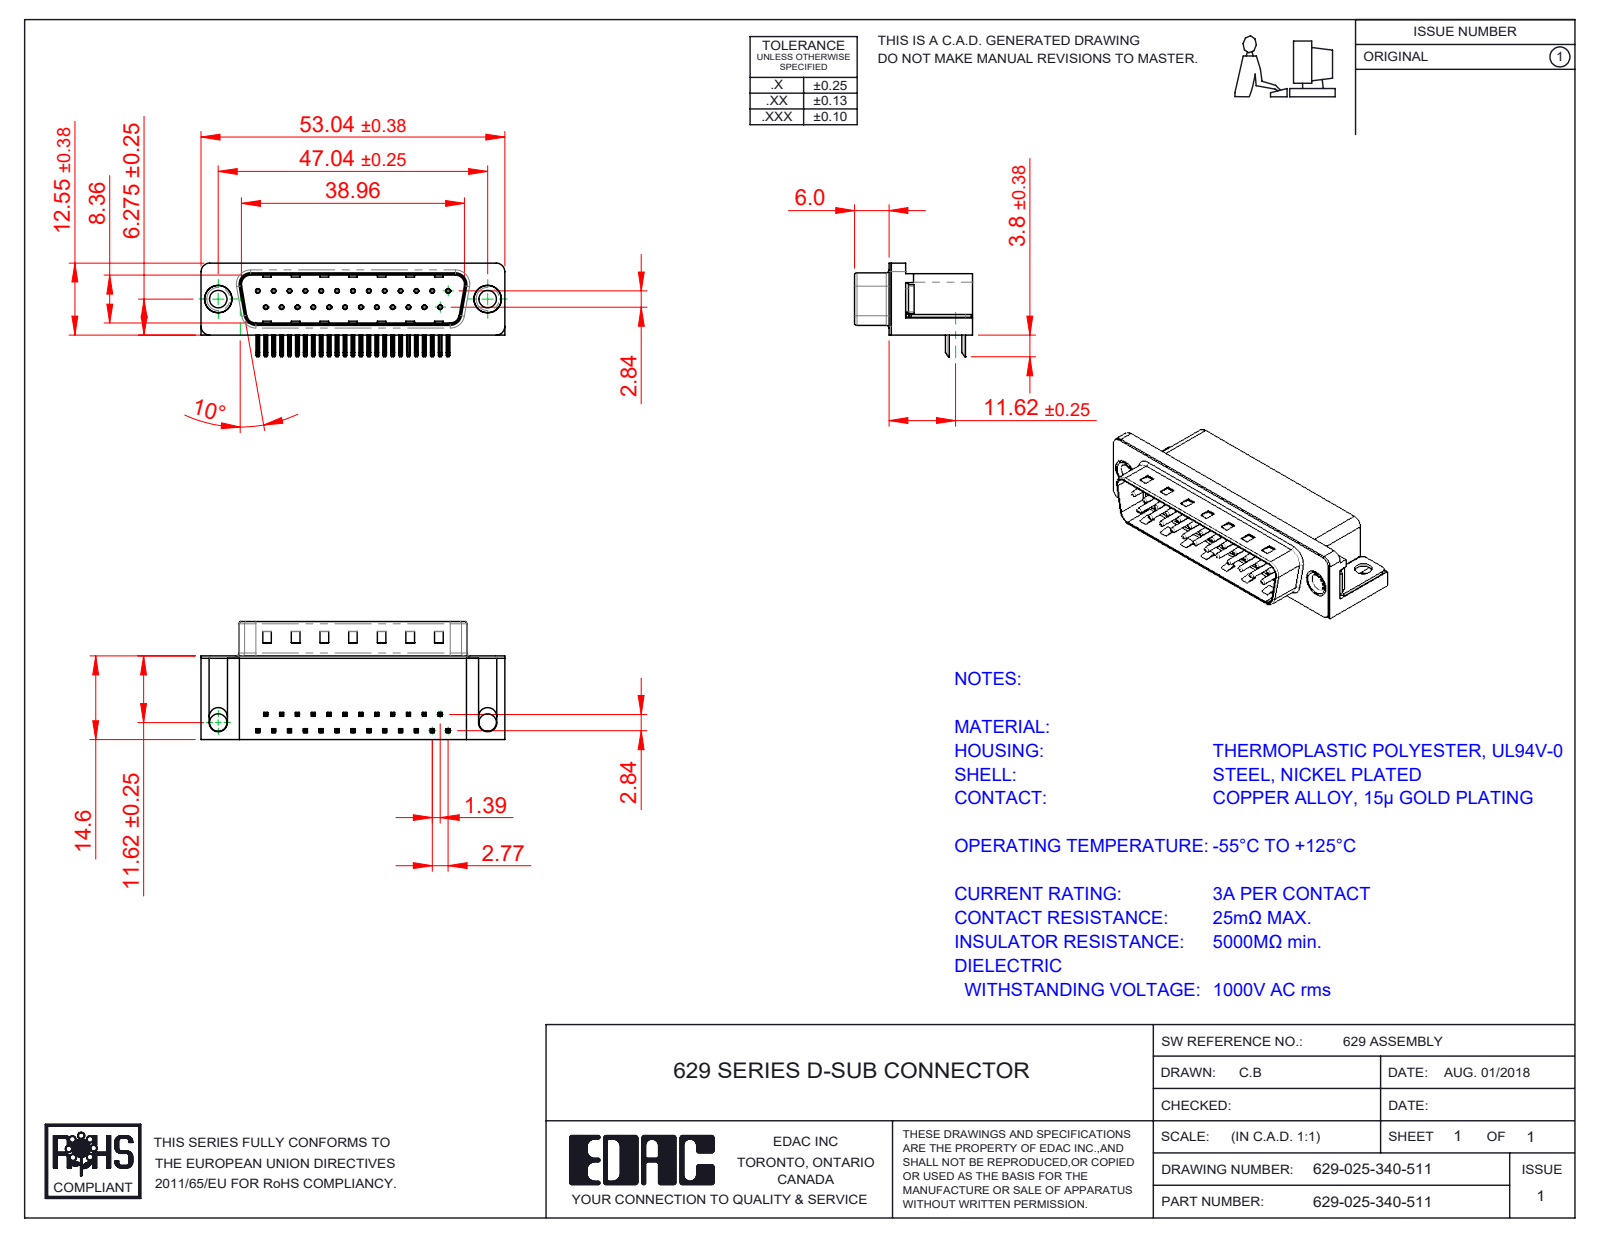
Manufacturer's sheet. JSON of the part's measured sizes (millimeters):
{"part_name": "629 Shell_25 Socket; 629-025-340-511; 629 Contact Bottom; 629 Thru Hole Rivet (+3 more)", "step_written_by": "SolidWorks 2020 (CONFIG_CONTROL_DESIGN)", "units": "millimeters", "bodies": {"solids": 31, "faces": 2221, "planar": 1403, "cylindrical": 641, "other": 177}, "overall_size": [53.04, 20.6, 16.35], "volume_mm3": 7310, "surface_area_mm2": 8191, "round_holes": [[0.35, 25], [0.8, 25], [3.05, 4], [4, 2], [4.8, 2], [5, 2]], "round_bosses_or_shafts": [[0.75, 25], [4.9, 2], [4.75, 2], [3.85, 2]], "partial_cylinders_radius": [[0.25, 108], [0.12, 50], [1, 16], [0.5, 9], [1.6, 8], [1.5, 7], [0.9, 4], [2, 4]], "face_to_face_distances": [0.4, 10.36, 14.2, 2.1, 8.76, 1.7, 10.46, 10.86, 14.6, 2.9], "hole_center_spacings": [3.16, 2.77, 5.54, 8.31, 11.08, 13.85, 16.62, 5.03]}
